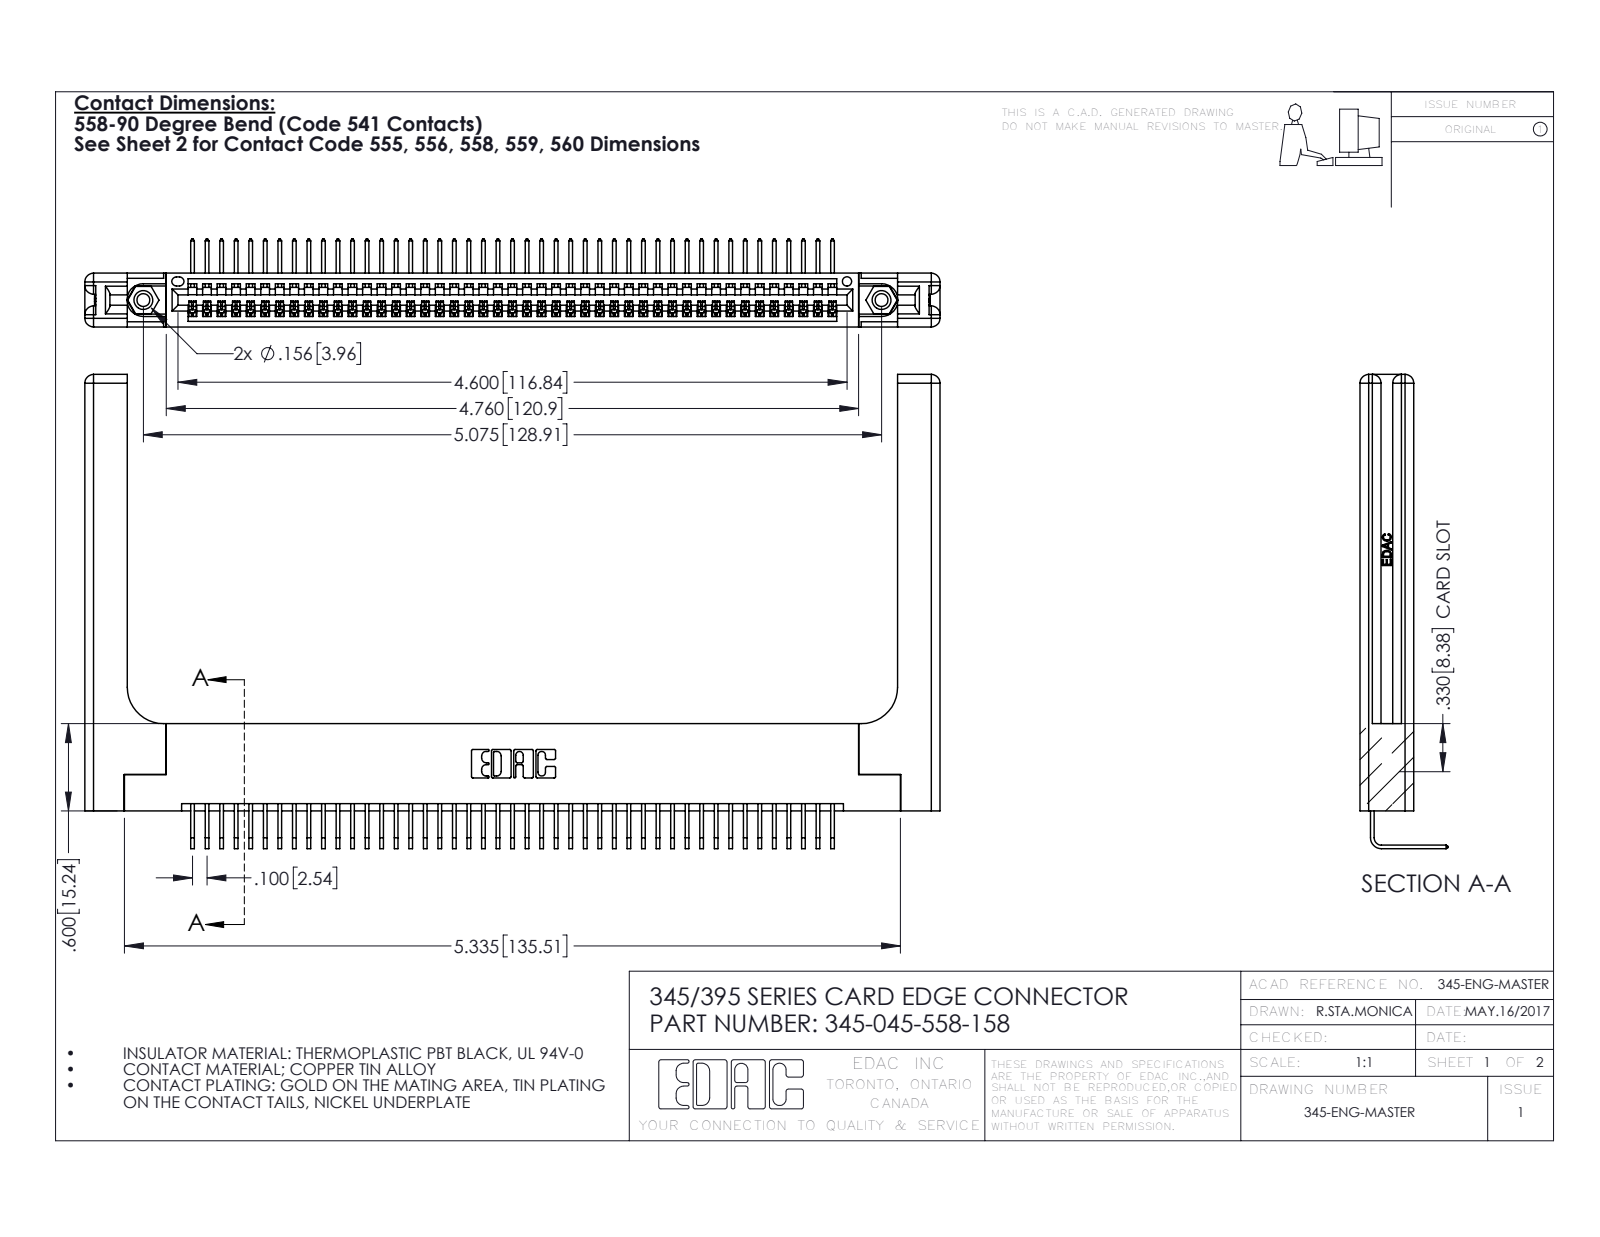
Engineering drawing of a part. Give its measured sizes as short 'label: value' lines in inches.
name: 345-292-001_558 Tail - 2; 345 Part_Flush Mounting Lugs - 0.156 Dia-TH; 345-220-058_345-220-058; 345-250-001_345-250-001-102 (+1 more)
written by: SolidWorks 2016 (CONFIG_CONTROL_DESIGN)
unit: in
bodies: 50 solids, 3082 faces (2118 planar, 904 cylindrical, 60 other)
size: 5.879 × 3.259 × 0.605
volume: 1.395 in³; area: 39.23 in²
holes: 2× ⌀0.089, 2× ⌀0.125, 2× ⌀0.156, 1× ⌀0.064
bosses: 2× ⌀0.155
rounds: 90× R0.006, 22× R0.01, 16× R0.06, 6× R0.007, 6× R0.031, 3× R0.026, 2× R0.03, 2× R0.031
face distances: 0.072, 0.37, 0.298, 0.2, 0.098, 0.272, 0.025, 0.225, 0.148, 0.15
hole spacings: 0.27, 4.839, 5.075
